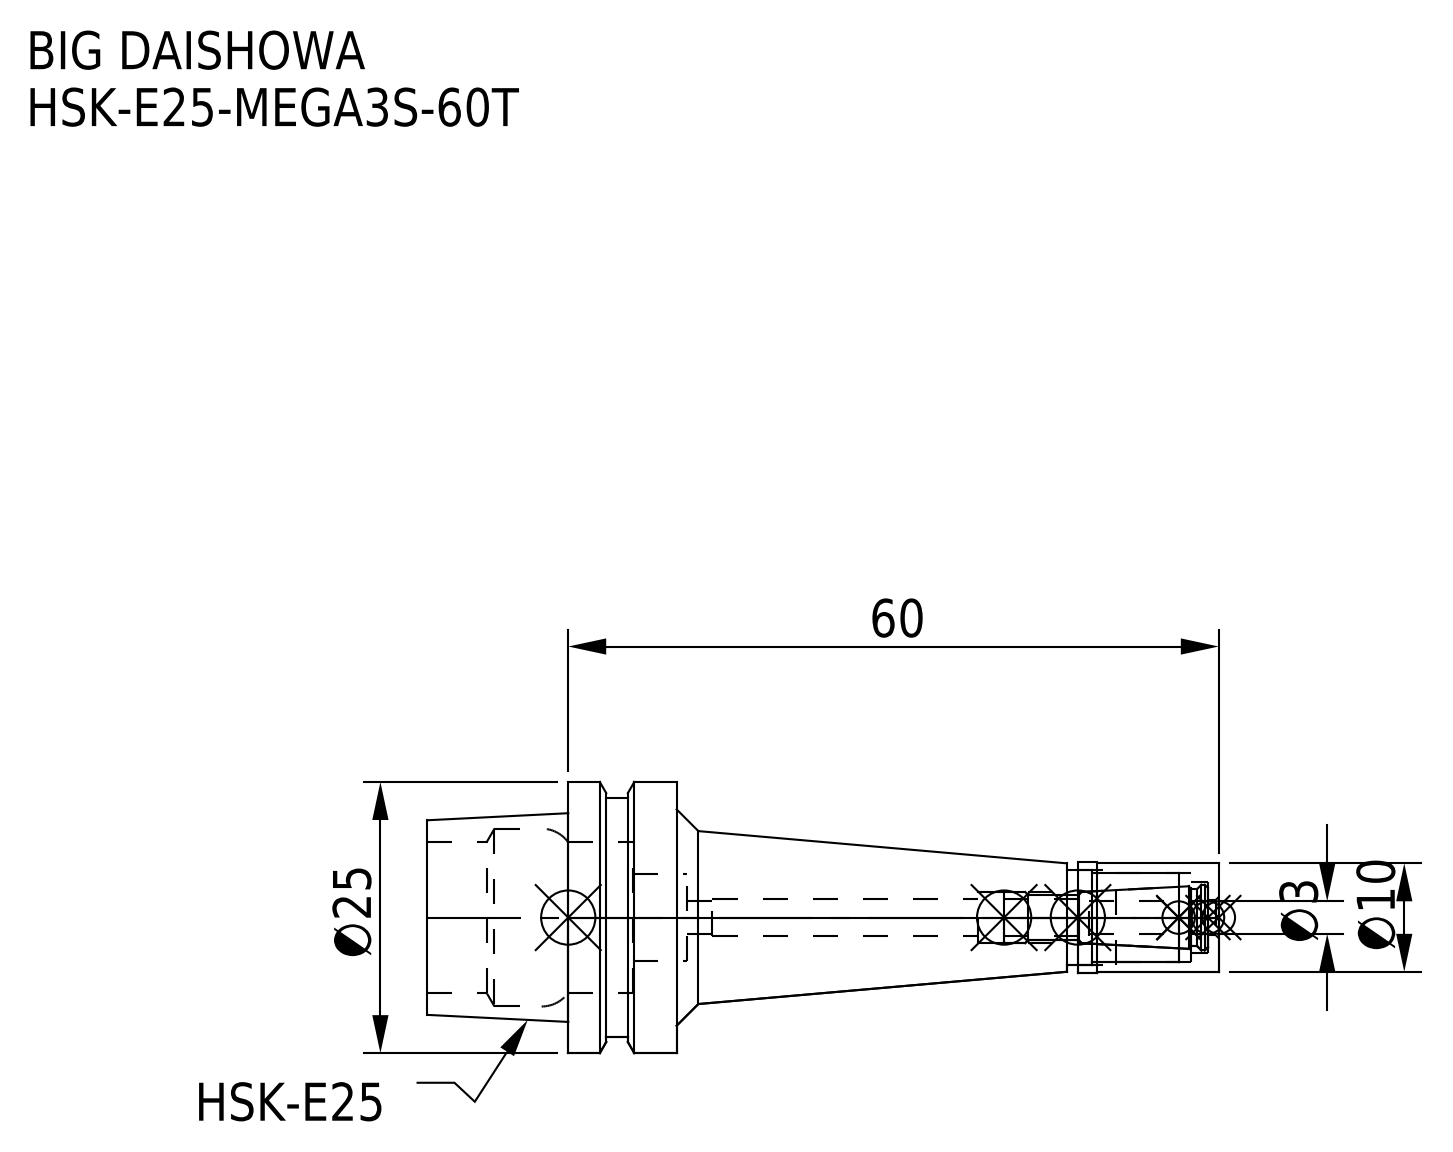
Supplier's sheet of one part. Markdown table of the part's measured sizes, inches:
| quantity | value |
| --- | --- |
| part name | HSK-E25-MEGA3S-60T-030-FreeParts; HSK-E25-MEGA3S-60T_1.stp; MGN3S_1.stp; DXF_TEMP_ASSY_ASM_4_ASM.stp (+3 more) |
| STEP written by | SolidWorks 2019 (CONFIG_CONTROL_DESIGN) |
| units | inches |
| bodies | 2 solids, 74 faces (18 planar, 38 cylindrical, 18 other) |
| overall size | 2.874 × 0.984 × 0.984 |
| volume | 0.615 in³ |
| surface area | 10.37 in² |
| round holes (diameter × count) | 0.118 × 1, 0.13 × 1, 0.134 × 1, 0.185 × 1, 0.26 × 1, 0.315 × 1, 0.323 × 1, 0.343 × 1, 0.551 × 1, 0.646 × 1 |
| round bosses / shafts (diameter × count) | 0.984 × 1, 0.866 × 1, 0.406 × 1, 0.394 × 1 |
| main face-to-face distances | 0.394, 0.512, 0.159, 0.234, 0.906, 0.746, 2.362, 1.969, 2.128, 2.874 |
